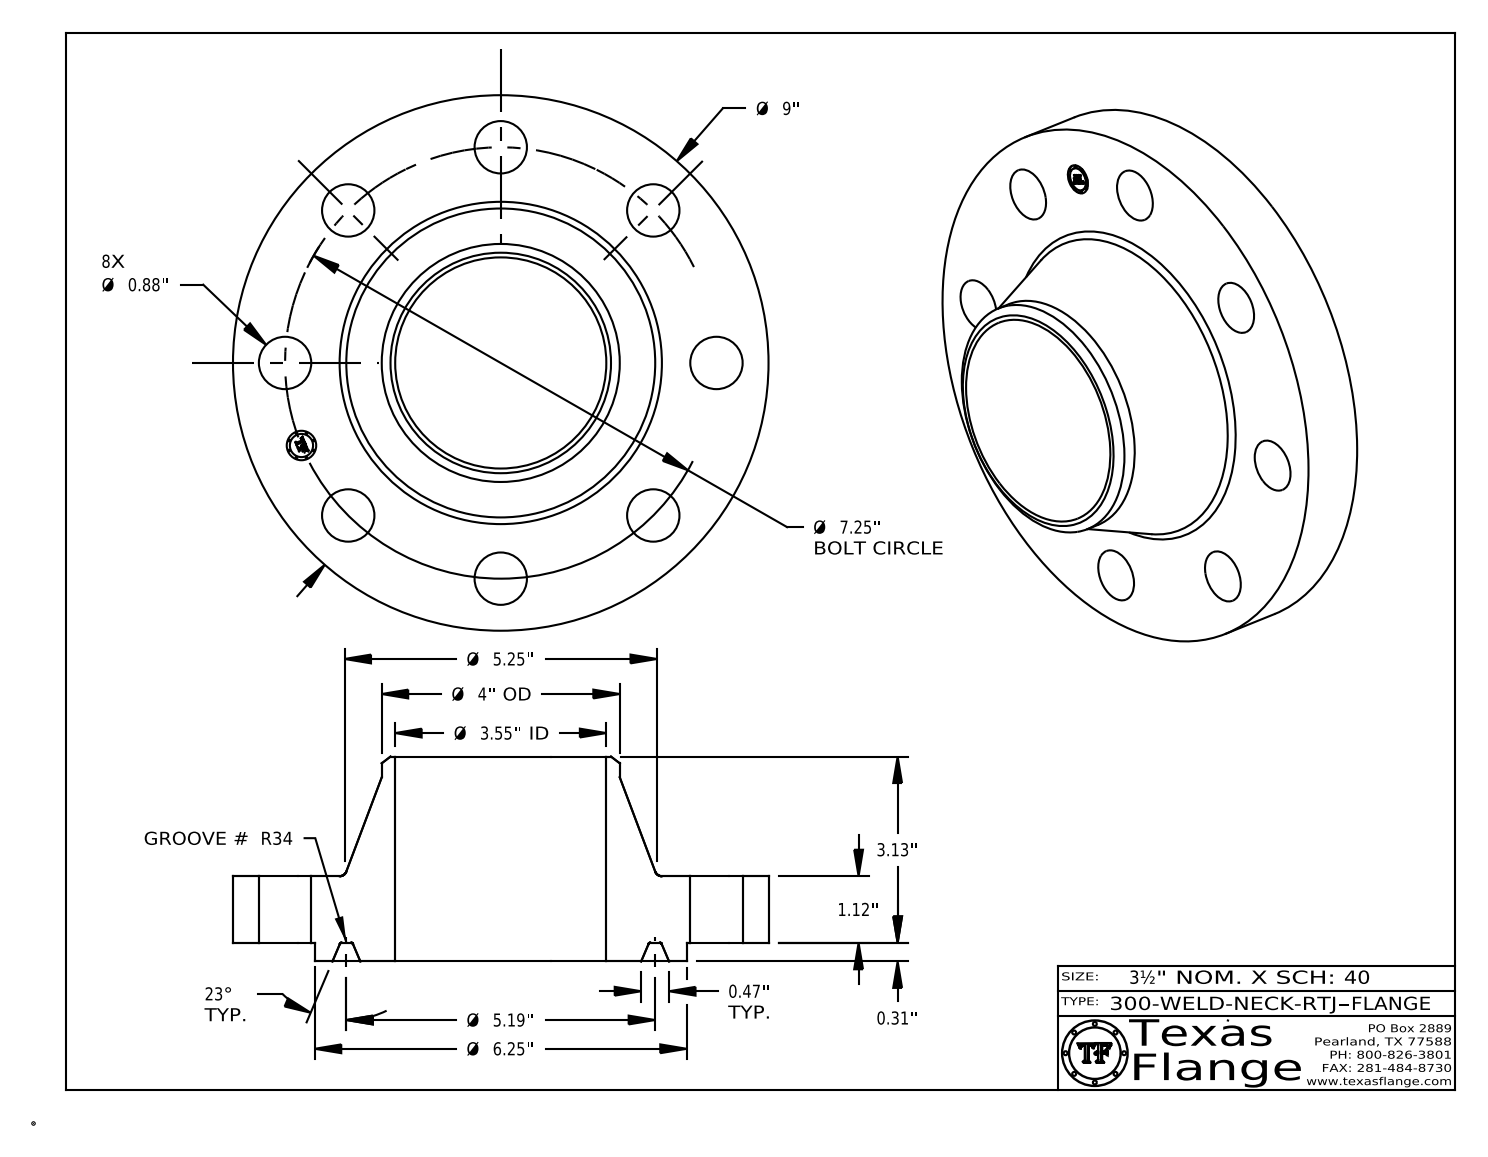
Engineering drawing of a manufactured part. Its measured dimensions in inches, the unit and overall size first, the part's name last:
Units: inches
Overall size (bounding box): 9 × 9 × 3.443
Round holes (diameter × count): ⌀0.88 ×8, ⌀0.495 ×1, ⌀3.548 ×1
Round bosses / shafts (diameter × count): ⌀0.03 ×8, ⌀9 ×1, ⌀6.25 ×1, ⌀4 ×1, ⌀0.39 ×1
Main face-to-face distances: 1.12, 0.313, 1.433, 3.443, 3.13, 2.01, 1.418, 1.105, 0.015, 2.025
Hole centre spacings: 3.625, 2.774, 5.127, 6.698, 7.25, 1.415, 7.111, 4.028
Volume: 72.03 in³ · Surface area: 225.2 in²
Bodies: 1 solid, 429 faces (371 planar, 44 cylindrical, 14 other)
Part name (STEP PRODUCT): 300-WELD-NECK-RTJ
STEP written by: CATIA V5 STEP AP214 (AUTOMOTIVE_DESIGN)
